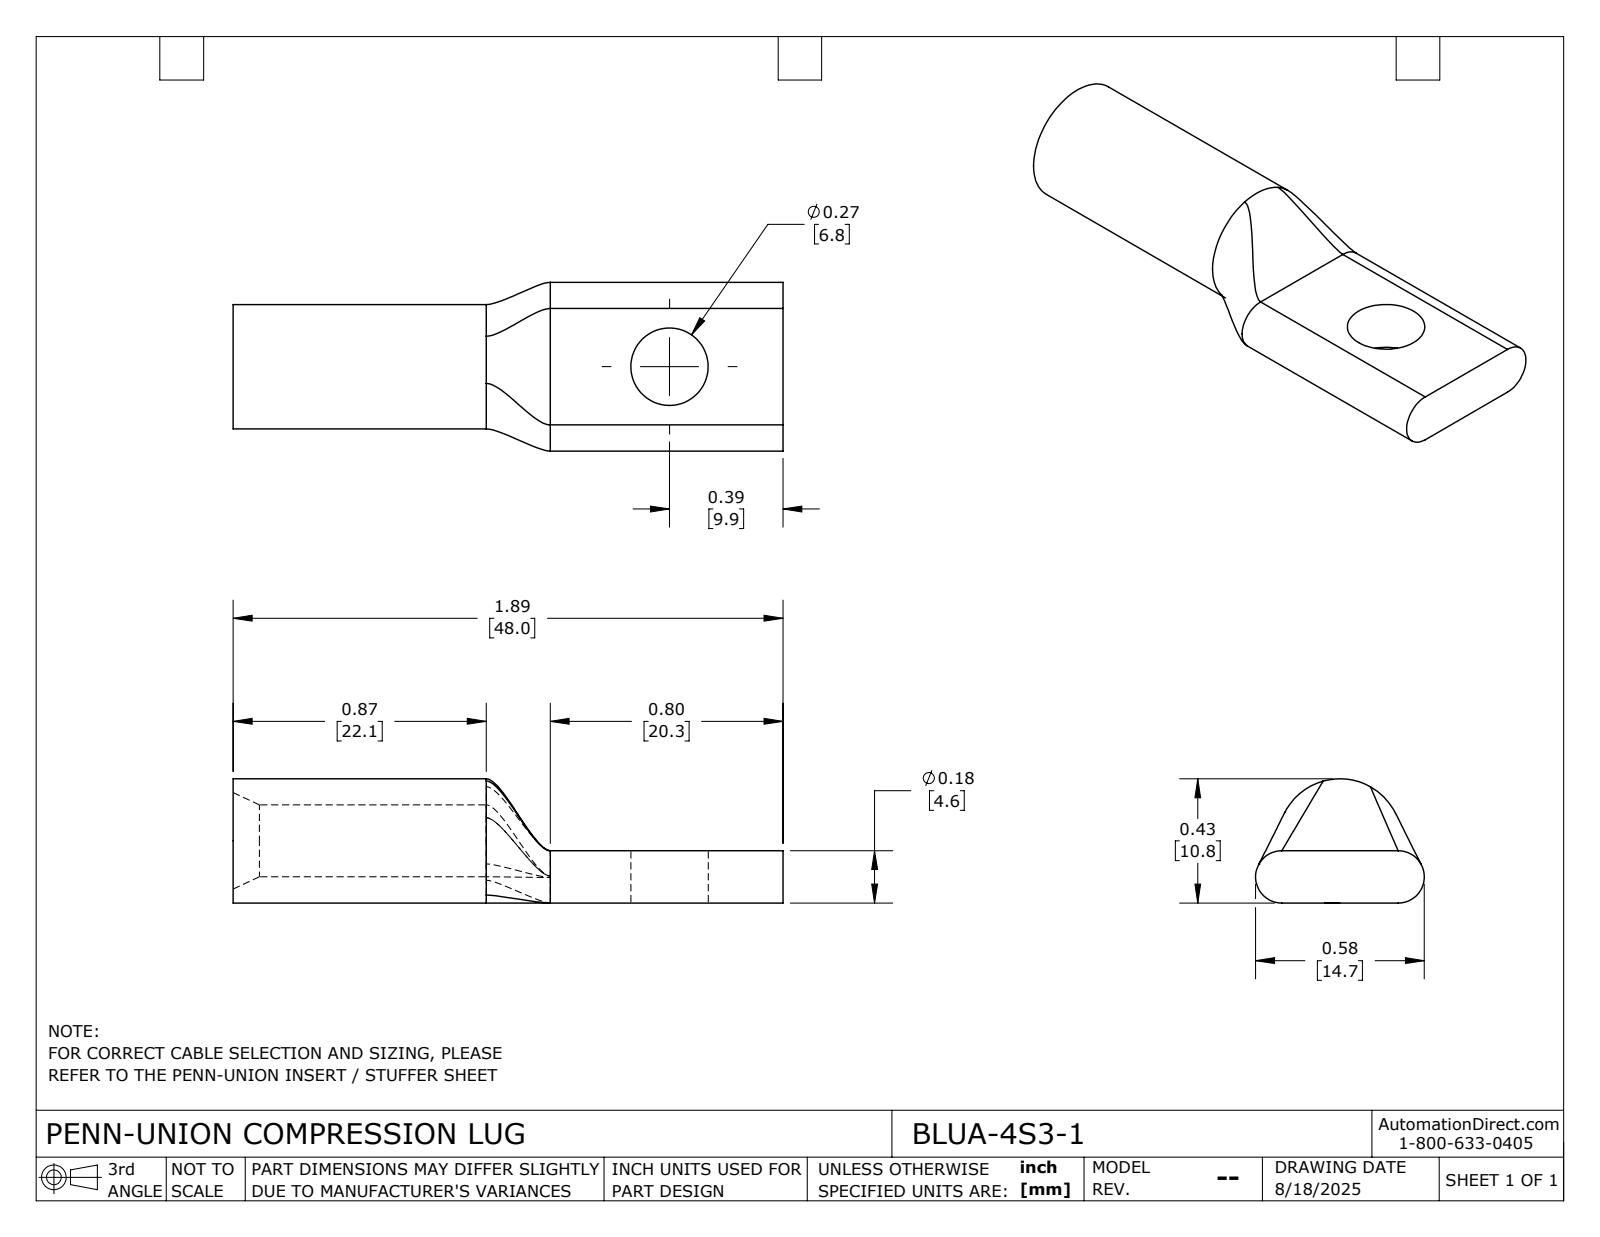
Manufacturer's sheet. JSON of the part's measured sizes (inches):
{"part_name": "BLUA-4S3-1", "step_written_by": "SolidWorks 2024 (CONFIG_CONTROL_DESIGN)", "units": "inches", "bodies": {"solids": 1, "faces": 24, "planar": 5, "cylindrical": 9, "other": 10}, "overall_size": [1.89, 0.58, 0.427], "volume_in3": 0.17, "surface_area_in2": 3.697, "round_holes": [[0.247, 1], [0.266, 1]], "round_bosses_or_shafts": [[0.427, 1]], "partial_cylinders_radius": [[0.09, 2]], "face_to_face_distances": [0.18, 1.89, 1.09, 0.8]}
